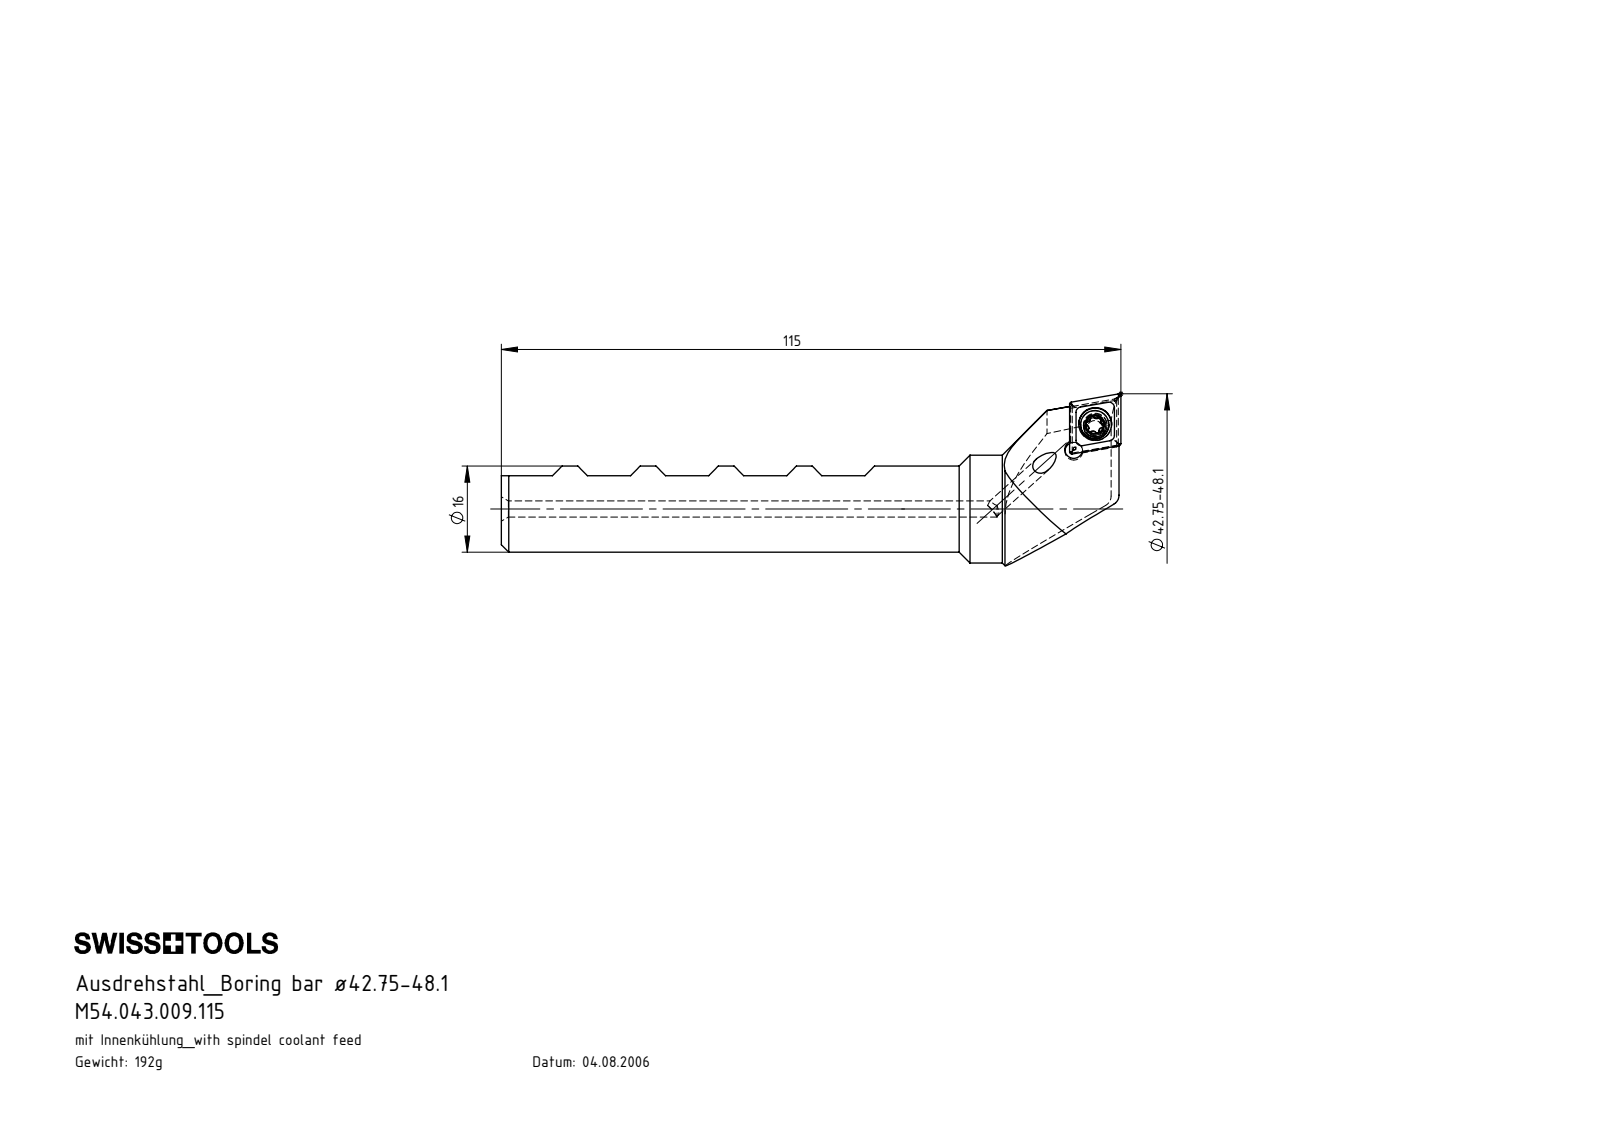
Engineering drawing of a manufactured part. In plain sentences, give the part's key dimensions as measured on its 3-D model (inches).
The part is named "CCMT09T304; B43.WCB.K11.115; B43-WCB.K11.115_A; WCB-ER2.001.009_A". Its 3-D file was written by "SolidWorks 2017 (AUTOMOTIVE_DESIGN)". It is 3 solids with 114 faces: 45 planar, 25 cylindrical and 44 other. Overall it measures 4.528 by 1.255 by 0.885 inches. Its volume is 1.49 cubic inches and its surface area 12.91 square inches. Round holes: 2 of diameter 0.118, 2 of diameter 0.13, 1 of diameter 0.173, 1 of diameter 0.24. Round bosses or shafts: 1 of diameter 0.787, 1 of diameter 0.63, 1 of diameter 0.207, 1 of diameter 0.157. Partial cylindrical surfaces (rounded edges, fillets, slot ends): 6 of radius 0.013, 6 of radius 0.023, 1 of radius 0.079, 1 of radius 0.413, 1 of radius 0.472. The main face-to-face distances are 0.33, 0.404, 0.479, 0.148, 0.807, 1.211, 0.807, 0.487, 0.156, 1.211. The hole center spacings are 0.239, 0.244.
